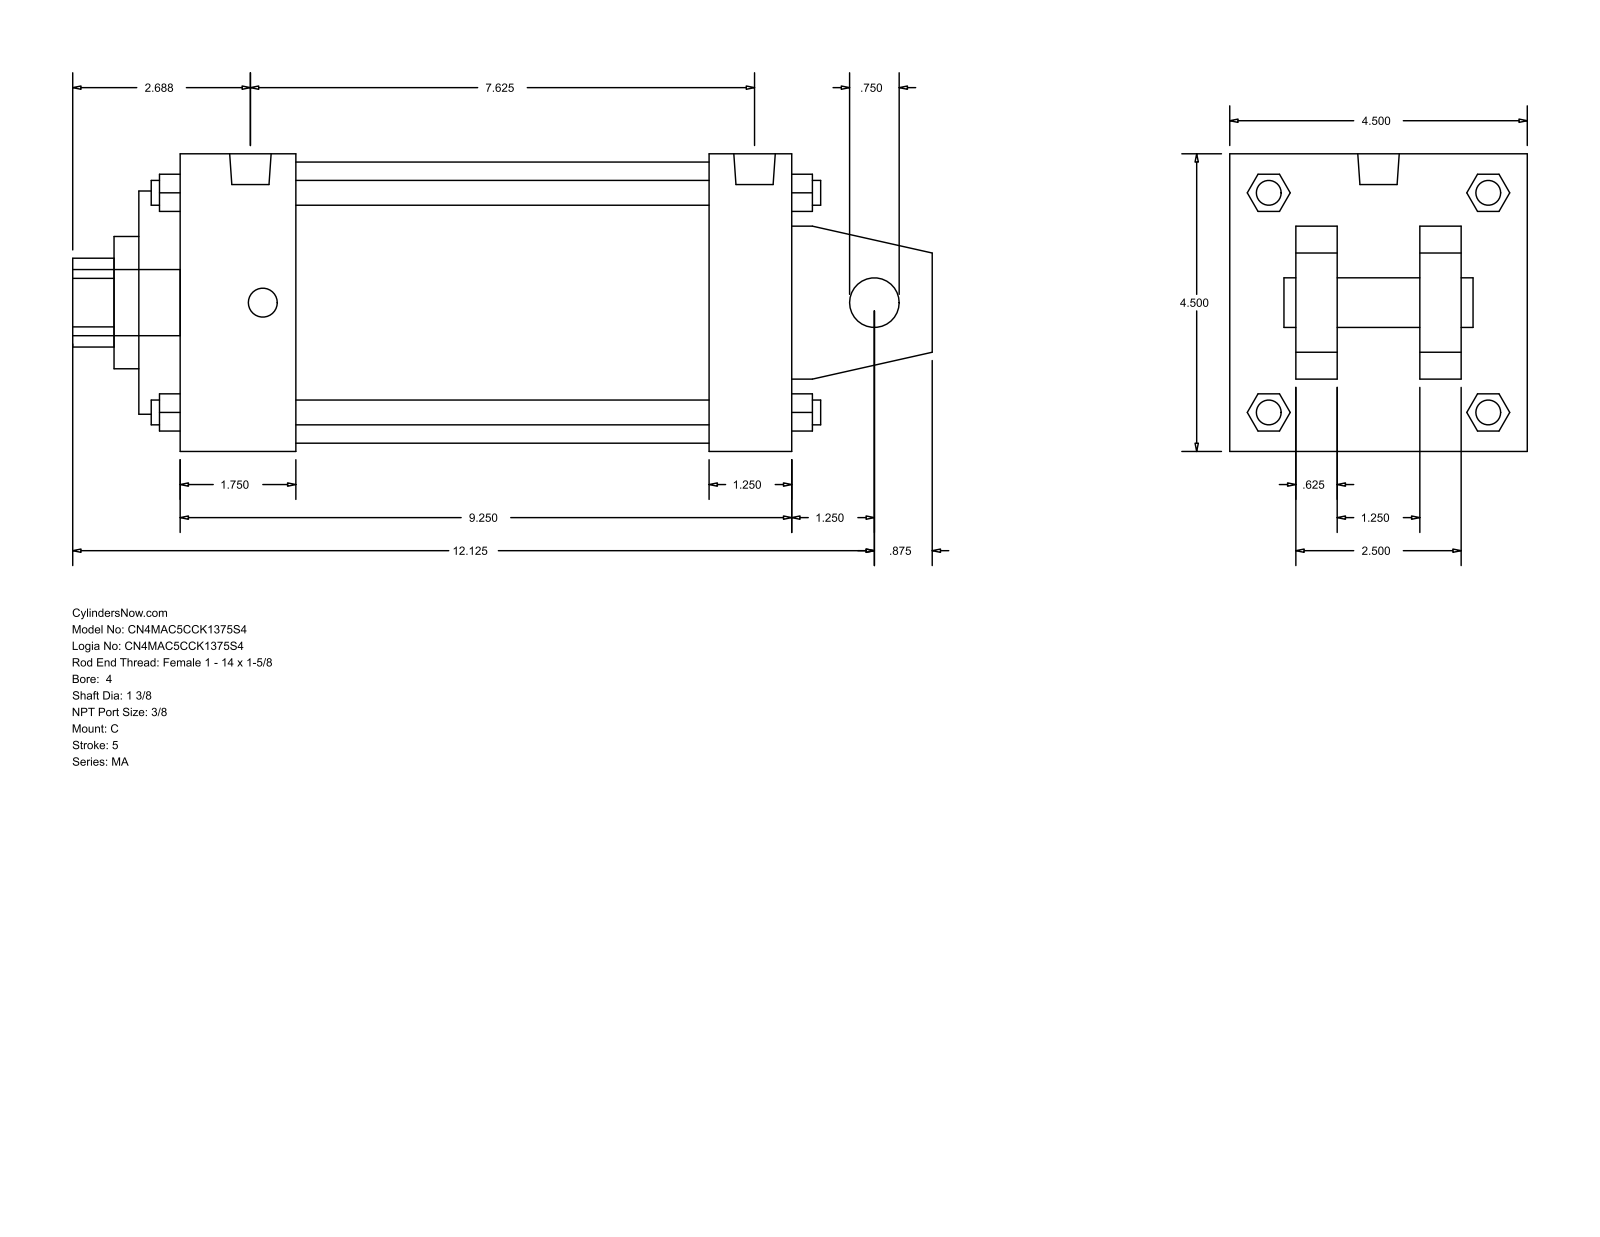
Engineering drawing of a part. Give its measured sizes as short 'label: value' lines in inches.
name: MA_C__0400_1.375
written by: GSSL Pune (CONFIG_CONTROL_DESIGN)
unit: in
bodies: 0 solids, 141 faces (109 planar, 32 cylindrical, 0 other)
size: 13 × 4.5 × 4.5
holes: 1× ⌀0.75, 1× ⌀1.375, 1× ⌀2, 1× ⌀3.375, 1× ⌀4.25
bosses: 4× ⌀0.437, 4× ⌀0.375, 2× ⌀0.627, 1× ⌀1
rounds: 1× R0.672
face distances: 4.5, 0.625, 9.25, 1.25, 2.875, 1.625, 1, 3.5, 1.875, 9.875
